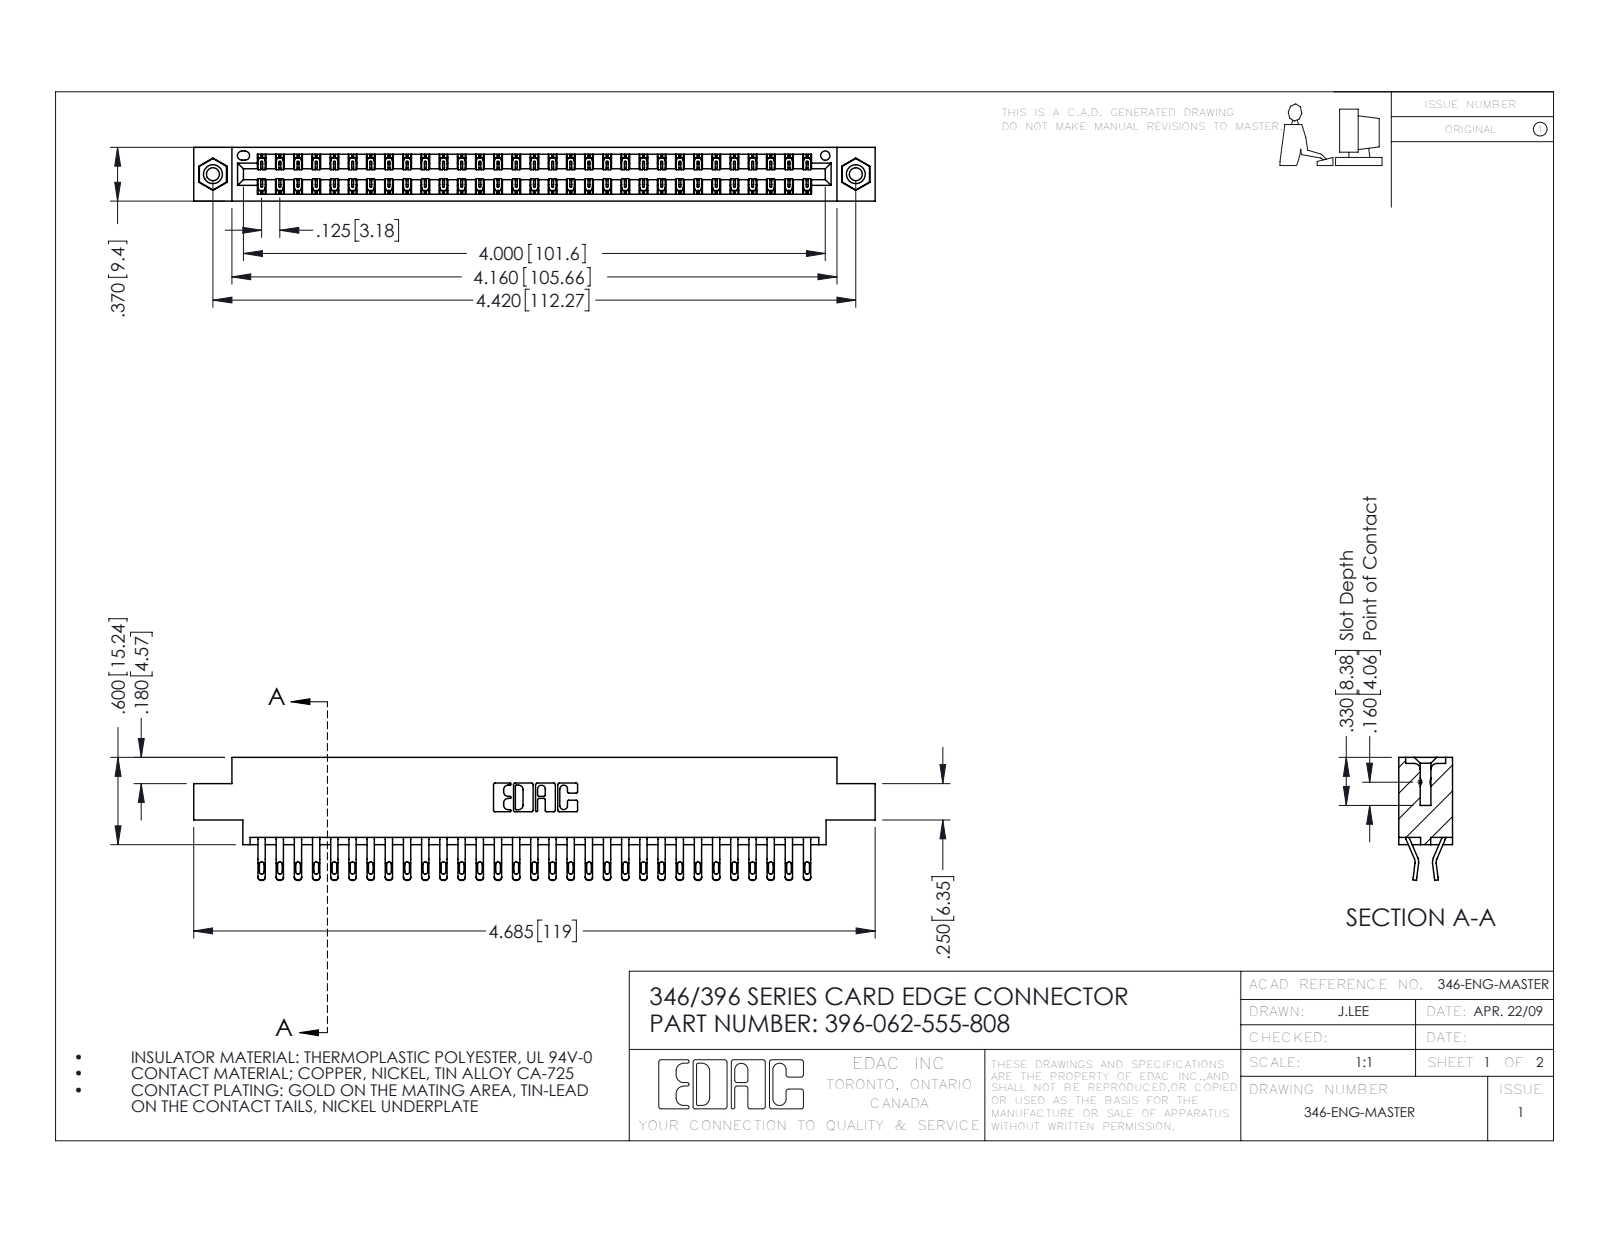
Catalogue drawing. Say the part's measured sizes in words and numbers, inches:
The part is named "396-062-555-808; 346 Part_0.170 Offset - 0.156 Dia-TI; 345-250-001_345-250-003-102; 345-292-001_555 Tail". Its 3-D file was written by "SolidWorks 2016 (CONFIG_CONTROL_DESIGN)". It is 65 solids with 3782 faces: 2158 planar, 1608 cylindrical and 16 other. Overall it measures 4.685 by 0.845 by 0.37 inches. Its volume is 0.704 cubic inches and its surface area 25.62 square inches. Round holes: 2 of diameter 0.089, 2 of diameter 0.125, 2 of diameter 0.156, 1 of diameter 0.064. Round bosses or shafts: 2 of diameter 0.155. Partial cylindrical surfaces (rounded edges, fillets, slot ends): 124 of radius 0.016, 124 of radius 0.02, 93 of radius 0.006, 22 of radius 0.01, 6 of radius 0.007, 6 of radius 0.031, 3 of radius 0.026, 2 of radius 0.01. The main face-to-face distances are 0.048, 0.322, 0.37, 0.25, 0.025, 0.072, 0.298, 0.275, 0.222, 0.148. The hole center spacings are 0.246, 4.212, 4.42.
